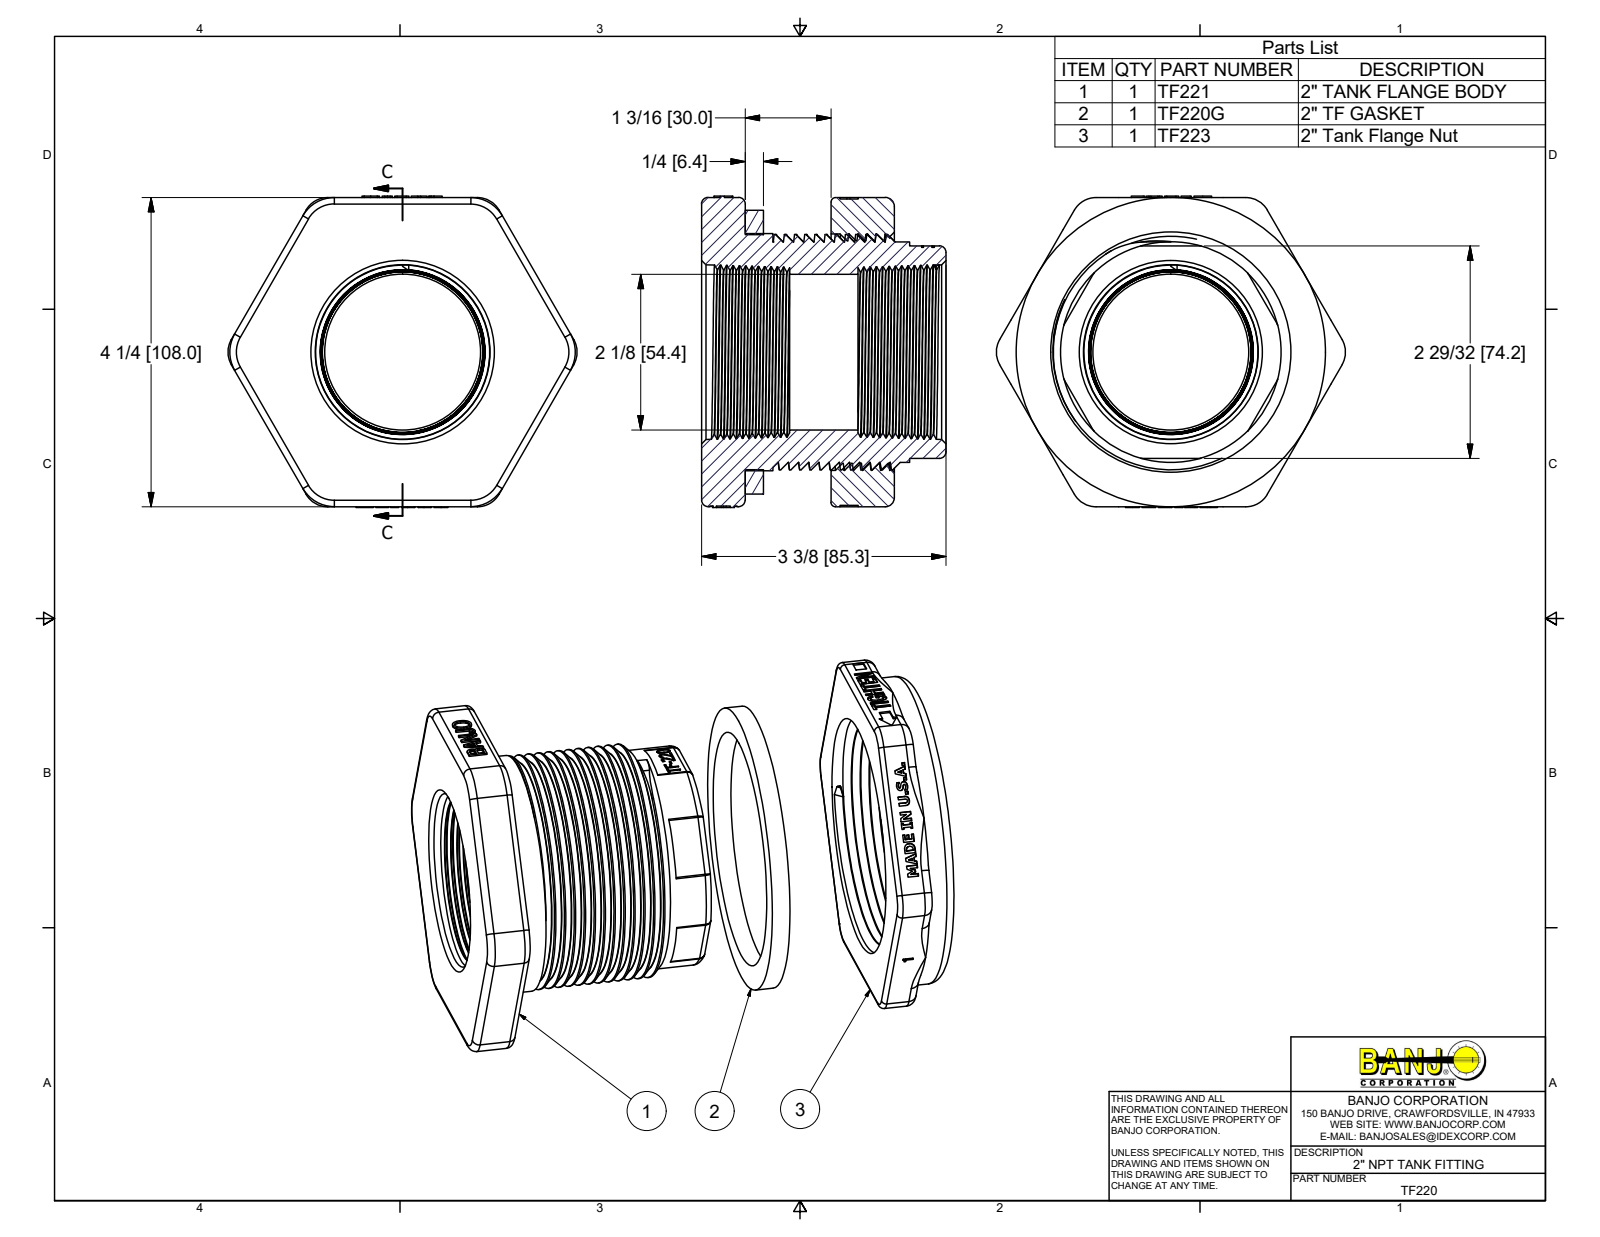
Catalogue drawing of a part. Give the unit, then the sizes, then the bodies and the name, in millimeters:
Units: millimetres
Overall size (bounding box): 121.95 × 108.71 × 85.34
Round holes (diameter × count): ⌀54.36 ×1, ⌀77.65 ×1, ⌀82.04 ×1, ⌀82.55 ×1
Round bosses / shafts (diameter × count): ⌀107.95 ×1, ⌀99.06 ×1, ⌀82.8 ×1, ⌀82.17 ×1, ⌀76.96 ×1
Partial cylindrical surfaces — rounded edges, fillets, slot ends (radius × count): R2.29 ×18, R1.52 ×12, R1.59 ×6, R3.17 ×6, R8.73 ×6, R12.7 ×6, R0.25 ×1, R25.4 ×1
Main face-to-face distances: 15.24, 45.21, 29.97, 67.31, 52.07, 22.1, 6.35, 21.59, 23.62, 45.72
Volume: 393 734 mm³ · Surface area: 105 900 mm²
Bodies: 3 solids, 878 faces (507 planar, 90 cylindrical, 281 other)
Part name (STEP PRODUCT): TF220; TF221; TF223; TF223X (+1 more)
STEP written by: Autodesk Inventor 2017 (AUTOMOTIVE_DESIGN)
